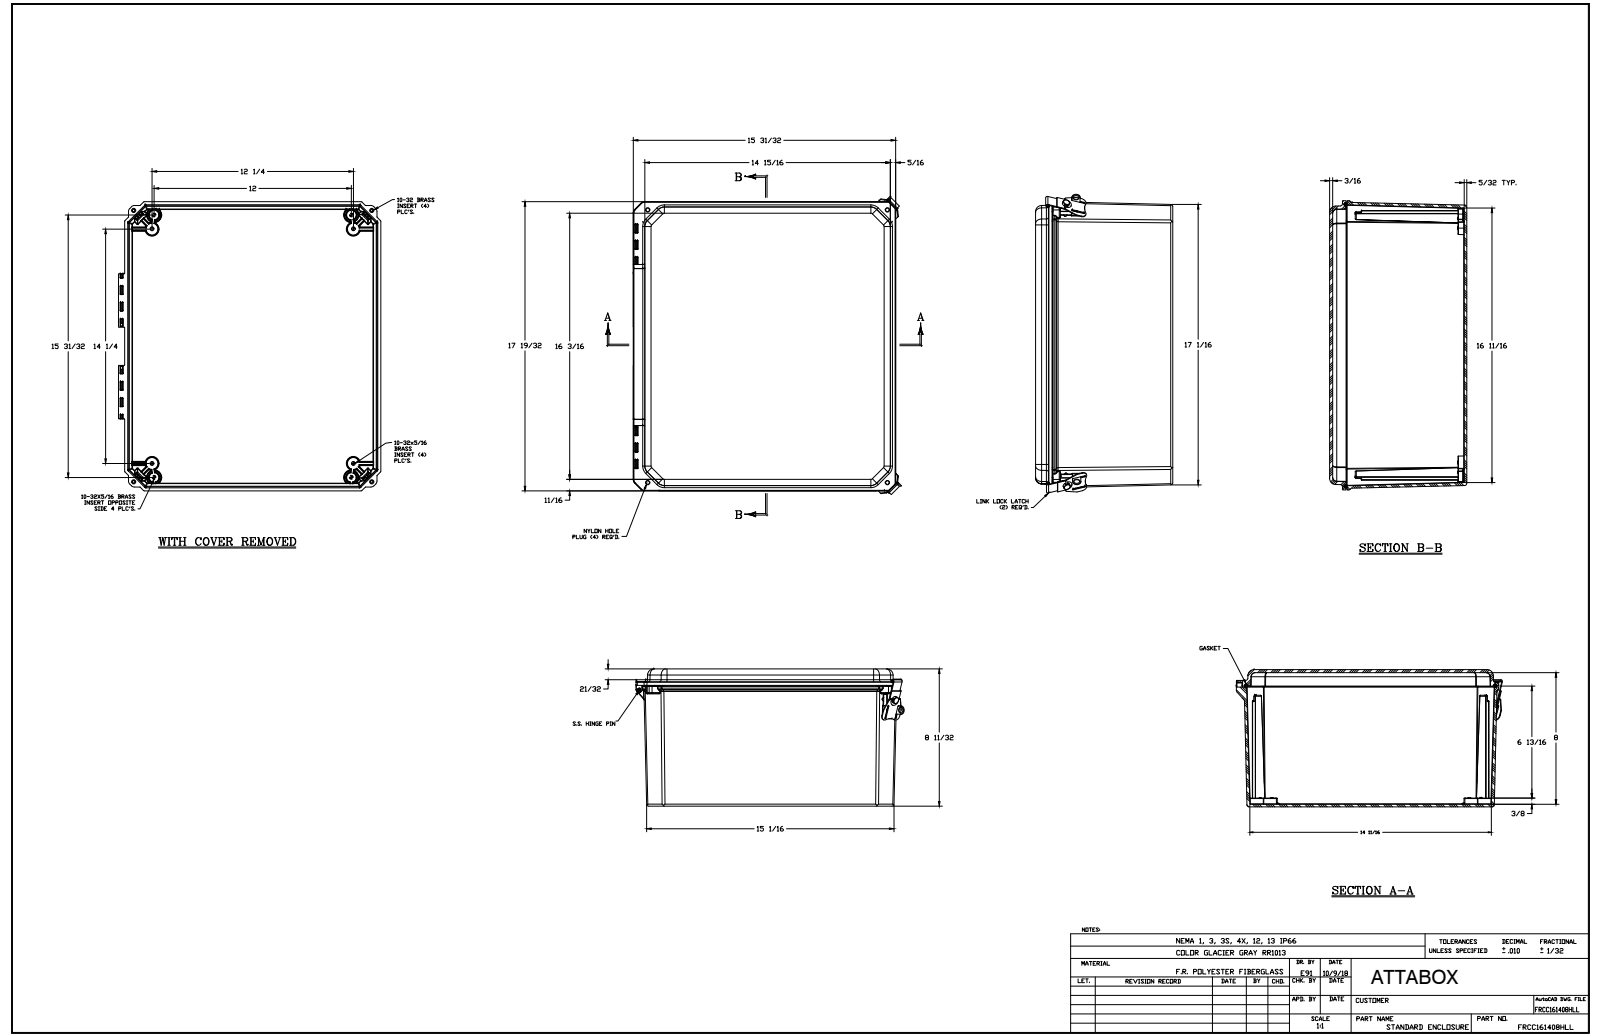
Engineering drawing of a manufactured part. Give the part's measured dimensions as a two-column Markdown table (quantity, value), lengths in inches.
| quantity | value |
| --- | --- |
| part name | FRCC161408HLL |
| STEP written by | SolidWorks 2018 (AUTOMOTIVE_DESIGN) |
| units | inches |
| bodies | 33 solids, 2367 faces (702 planar, 936 cylindrical, 729 other) |
| overall size | 18.471 × 16.406 × 8.343 |
| volume | 172.5 in³ |
| surface area | 2 214 in² |
| round holes (diameter × count) | 0.156 × 12, 0.152 × 8, 0.098 × 4, 0.15 × 4, 0.219 × 4, 0.252 × 4, 0.312 × 4, 0.05 × 2, 0.12 × 2, 0.363 × 2, 0.137 × 1 |
| round bosses / shafts (diameter × count) | 0.246 × 12, 0.209 × 4, 0.2 × 4, 0.135 × 3, 0.6 × 2, 0.05 × 2 |
| partial cylindrical surfaces (radius × count) | 0.01 × 222, 0.005 × 116, 0.02 × 59, 0.125 × 41, 0.03 × 36, 0.039 × 28, 0.25 × 26, 0.03 × 24 |
| main face-to-face distances | 0.156, 0.125, 8.218, 8.062, 8.343, 8.187, 0.18, 0.181, 0.125, 0.937 |
| hole center spacings | 15.461, 16.324, 16.584, 0.865, 15.106, 20.438, 0.793, 1.33 |
